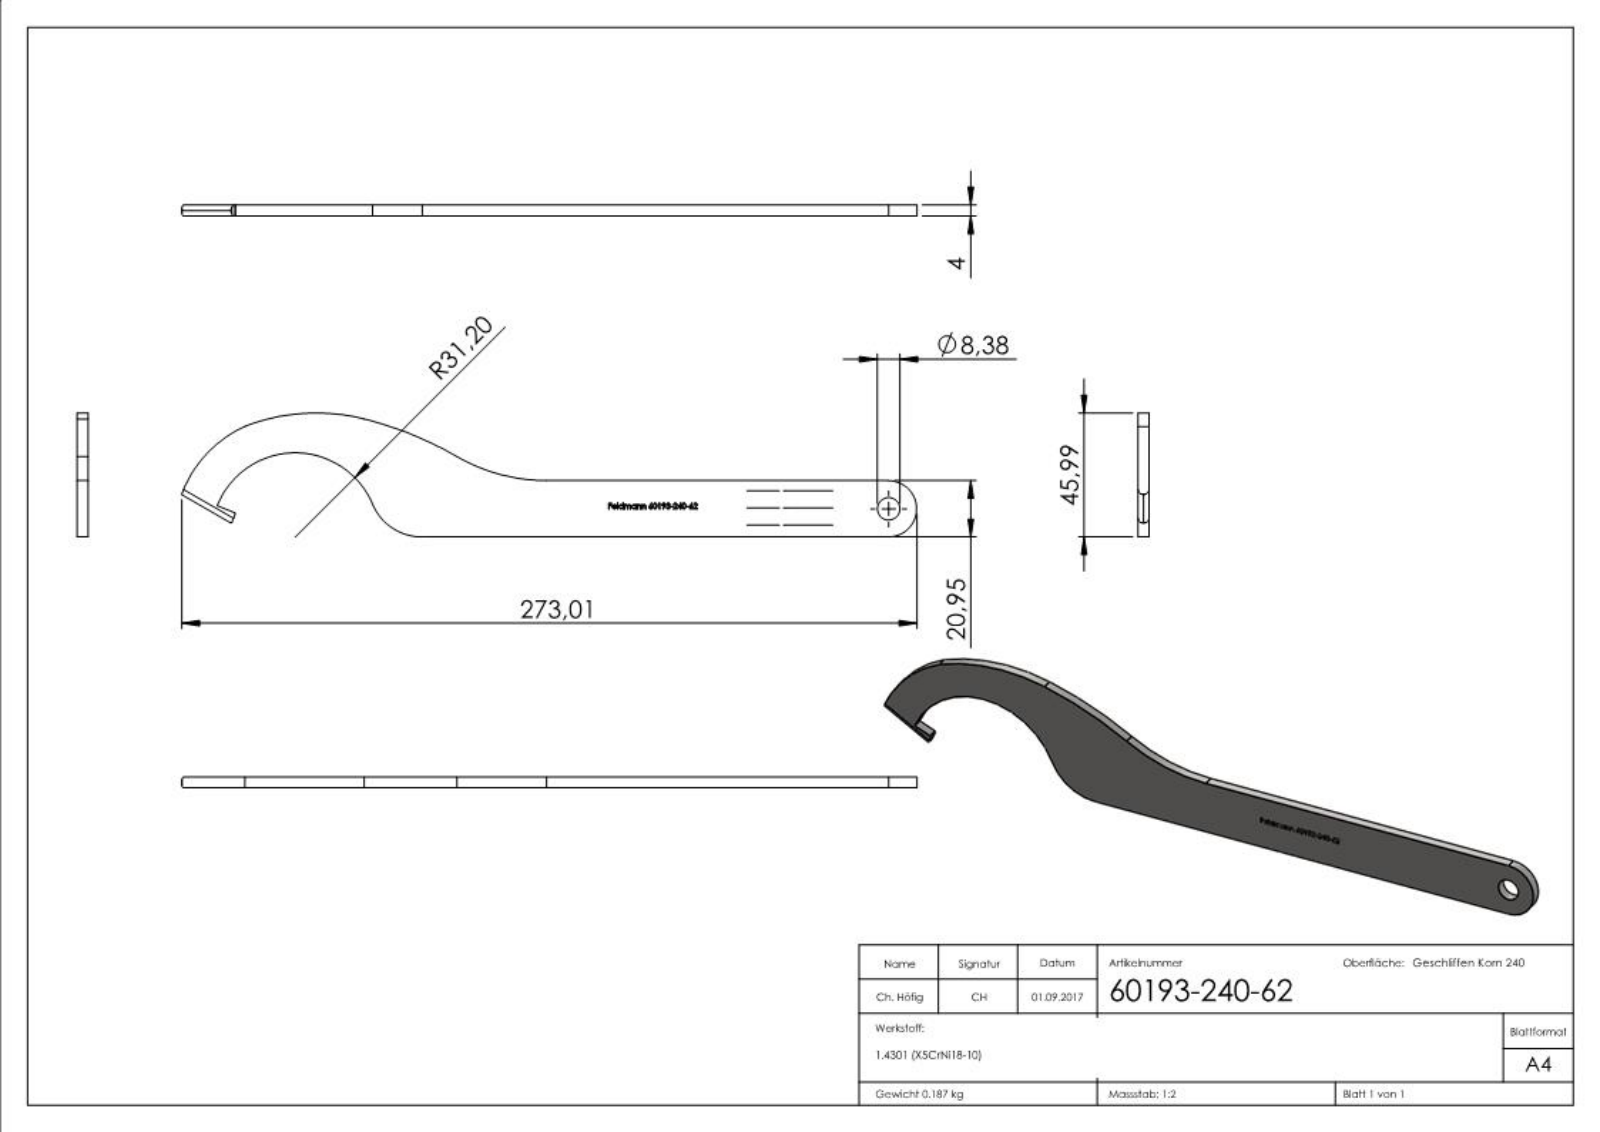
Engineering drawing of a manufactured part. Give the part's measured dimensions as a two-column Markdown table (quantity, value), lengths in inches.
| quantity | value |
| --- | --- |
| part name | 60193-240-62 |
| STEP written by | SolidWorks 2015 (CONFIG_CONTROL_DESIGN) |
| units | inches |
| bodies | 1 solid, 274 faces (140 planar, 15 cylindrical, 119 other) |
| overall size | 10.748 × 1.811 × 0.157 |
| volume | 1.441 in³ |
| surface area | 22.28 in² |
| round holes (diameter × count) | 0.33 × 1 |
| partial cylindrical surfaces (radius × count) | 0.014 × 3, 0.079 × 1, 0.413 × 1, 0.787 × 1, 1.228 × 1, 1.775 × 1, 2.616 × 1, 2.882 × 1 |
| main face-to-face distances | 0.157, 0.825, 0.154, 0.413, 0.412, 0.612, 0.187, 0.127, 0.739, 0.017 |
